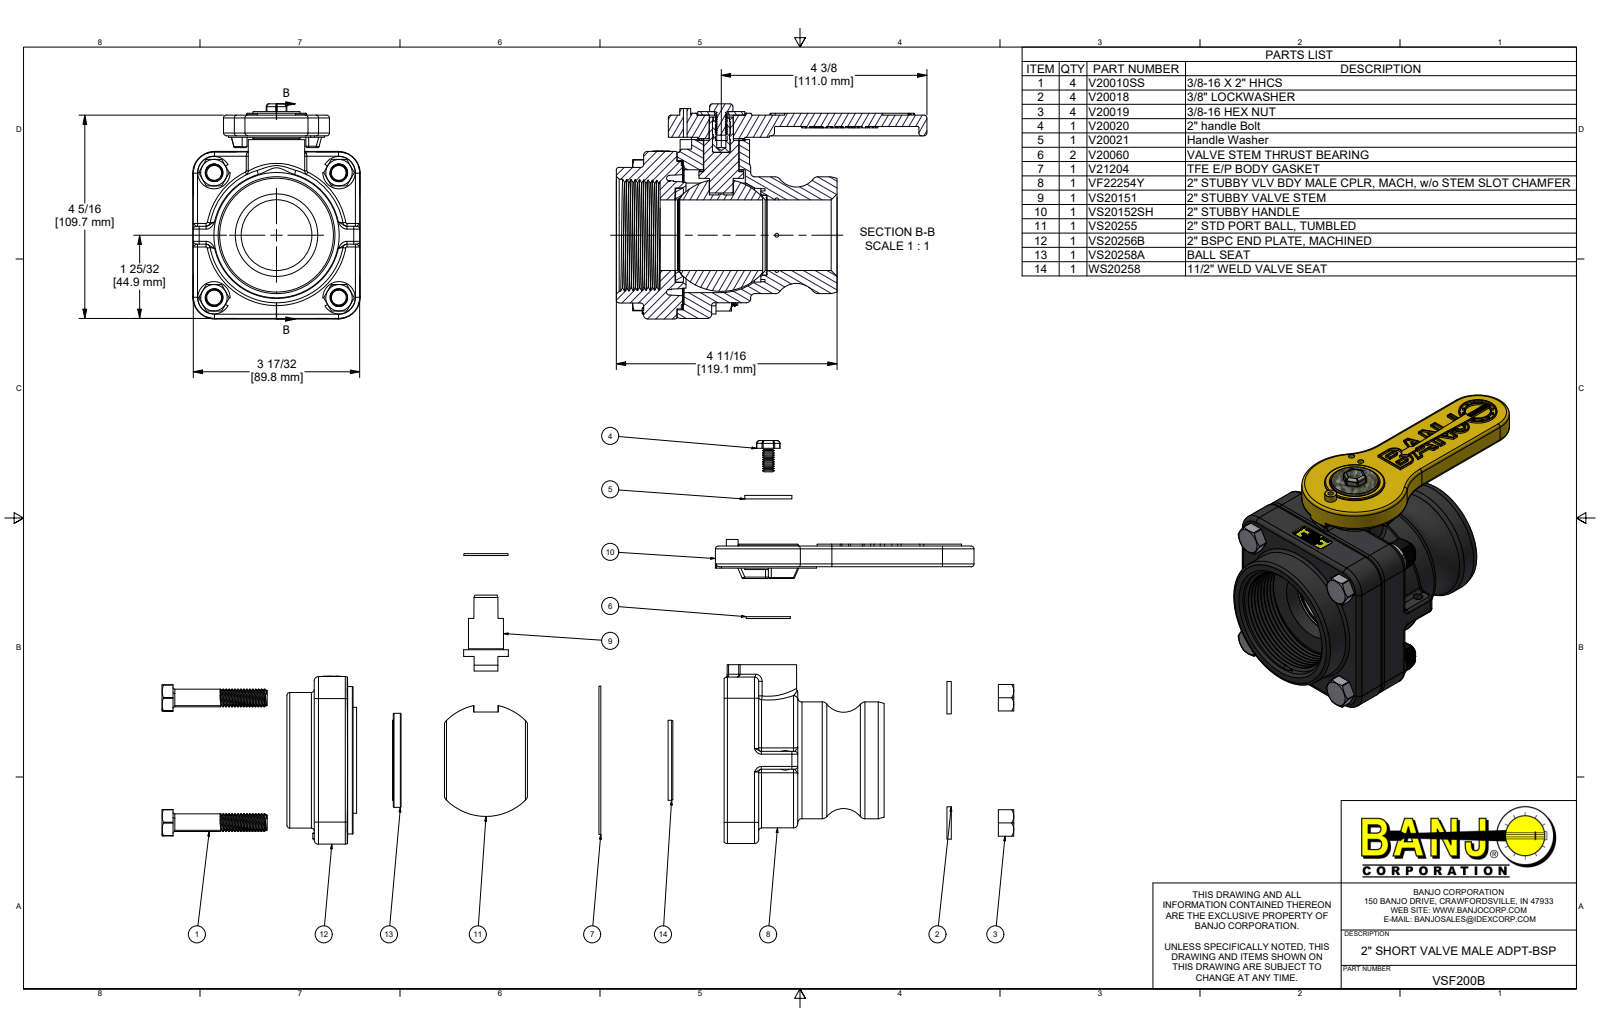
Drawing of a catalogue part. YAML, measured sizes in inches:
part_name: "VSF200B; V20010SS; V20018; V20019 (+8 more)"
step_written_by: "Autodesk Inventor 2022 (AUTOMOTIVE_DESIGN)"
units: inches
bodies: {solids: 26, faces: 2880, planar: 1262, cylindrical: 580, other: 1038}
overall_size: [6.6, 4.571, 3.56]
volume: 27.67
surface_area: 232
round_holes:
  - {diameter: 0.375, count: 5}
  - {diameter: 0.307, count: 4}
  - {diameter: 0.385, count: 4}
  - {diameter: 0.406, count: 4}
  - {diameter: 0.42, count: 4}
  - {diameter: 0.08, count: 2}
  - {diameter: 0.13, count: 2}
  - {diameter: 0.2, count: 2}
  - {diameter: 0.118, count: 1}
  - {diameter: 0.196, count: 1}
  - {diameter: 0.281, count: 1}
  - {diameter: 0.351, count: 1}
round_bosses_or_shafts:
  - {diameter: 0.324, count: 60}
  - {diameter: 0.687, count: 4}
  - {diameter: 0.375, count: 4}
  - {diameter: 3.15, count: 1}
  - {diameter: 3.13, count: 1}
  - {diameter: 2.88, count: 1}
  - {diameter: 2.482, count: 1}
  - {diameter: 2.25, count: 1}
partial_cylinders:
  - {radius: 0.06, count: 30}
  - {radius: 0.09, count: 20}
  - {radius: 0.03, count: 15}
  - {radius: 0.162, count: 8}
  - {radius: 0.125, count: 5}
  - {radius: 0.32, count: 4}
  - {radius: 0.45, count: 4}
  - {radius: 0.469, count: 4}
face_to_face_distances: [3.547, 0.013, 1.445, 0.71, 0.735, 0.02, 0.04, 3.56, 0.51, 0.23]
hole_center_spacings: [2.653, 1.872, 1.88, 2.648, 2.658, 3.752, 1.586, 1.749]
